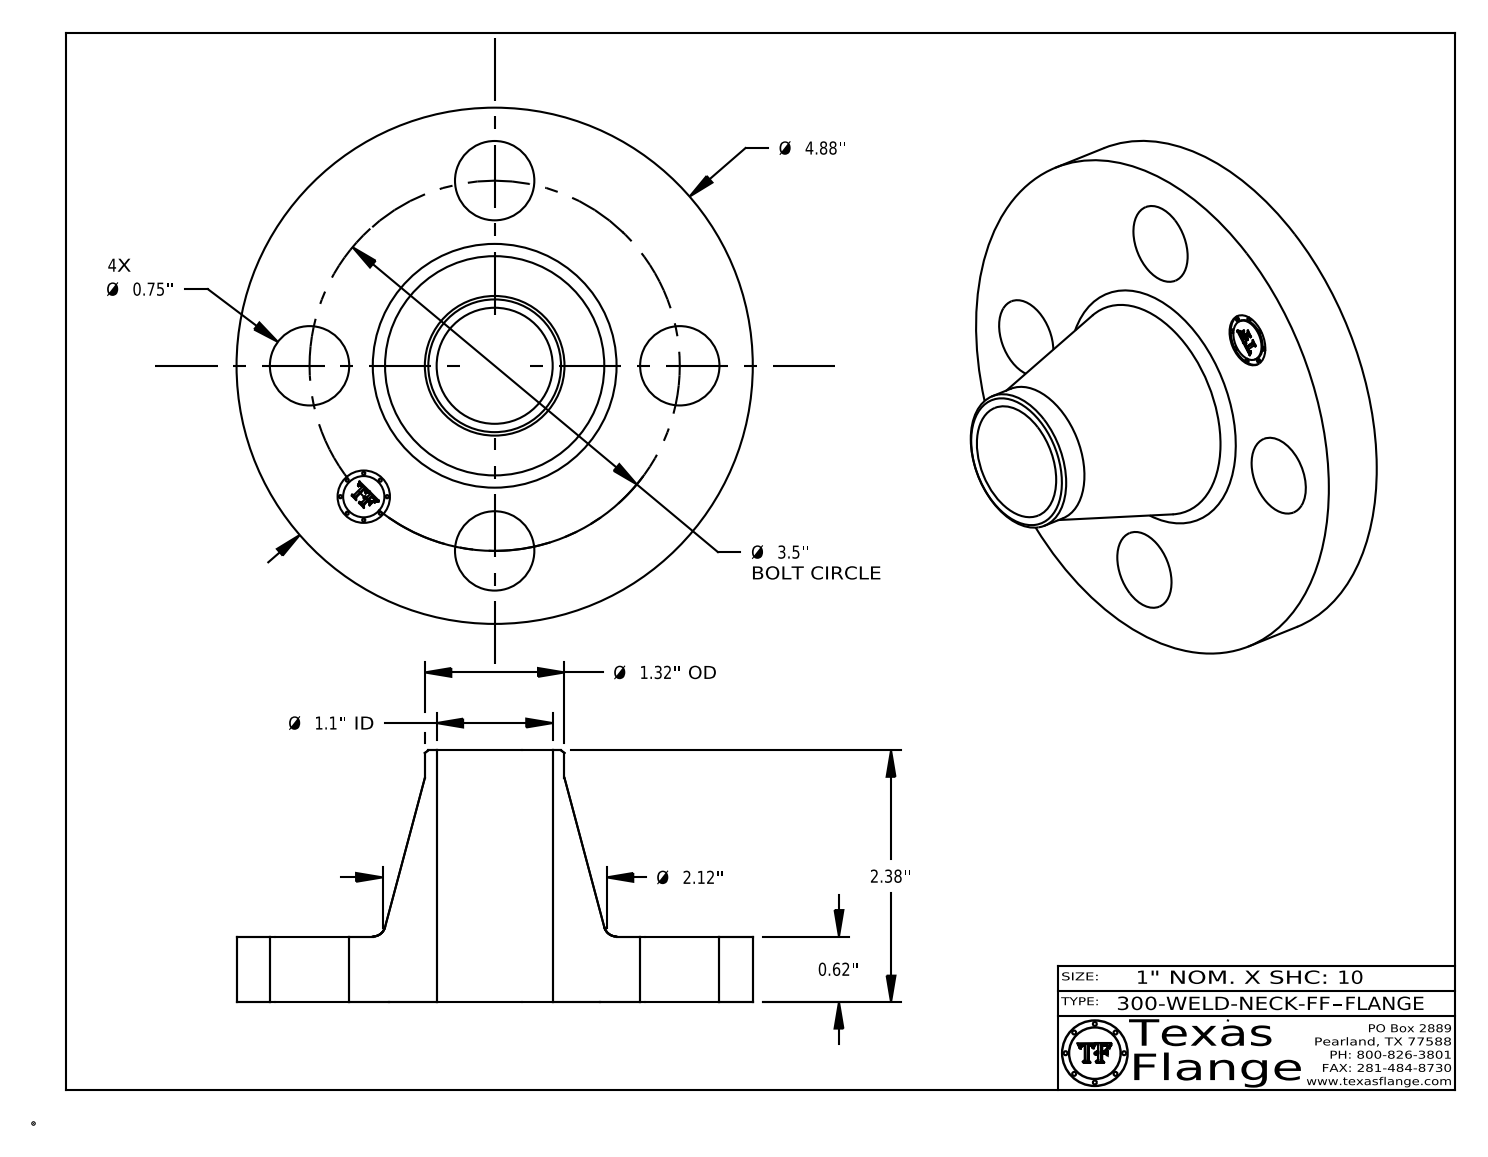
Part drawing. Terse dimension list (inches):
name: 300-WELD-NECK-FF
written by: CATIA V5 STEP AP214 (AUTOMOTIVE_DESIGN)
unit: in
bodies: 1 solid, 409 faces (369 planar, 34 cylindrical, 6 other)
size: 4.88 × 4.88 × 2.38
volume: 12.16 in³; area: 62.68 in²
holes: 4× ⌀0.75, 1× ⌀0.495, 1× ⌀1.097
bosses: 8× ⌀0.03, 1× ⌀4.88, 1× ⌀1.32, 1× ⌀0.39
face distances: 0.62, 2.38, 1.76, 0.015, 0.605, 1.775, 0.148, 0.145, 0.027, 0.096
hole spacings: 1.75, 2.475, 1.339, 3.233, 3.5
